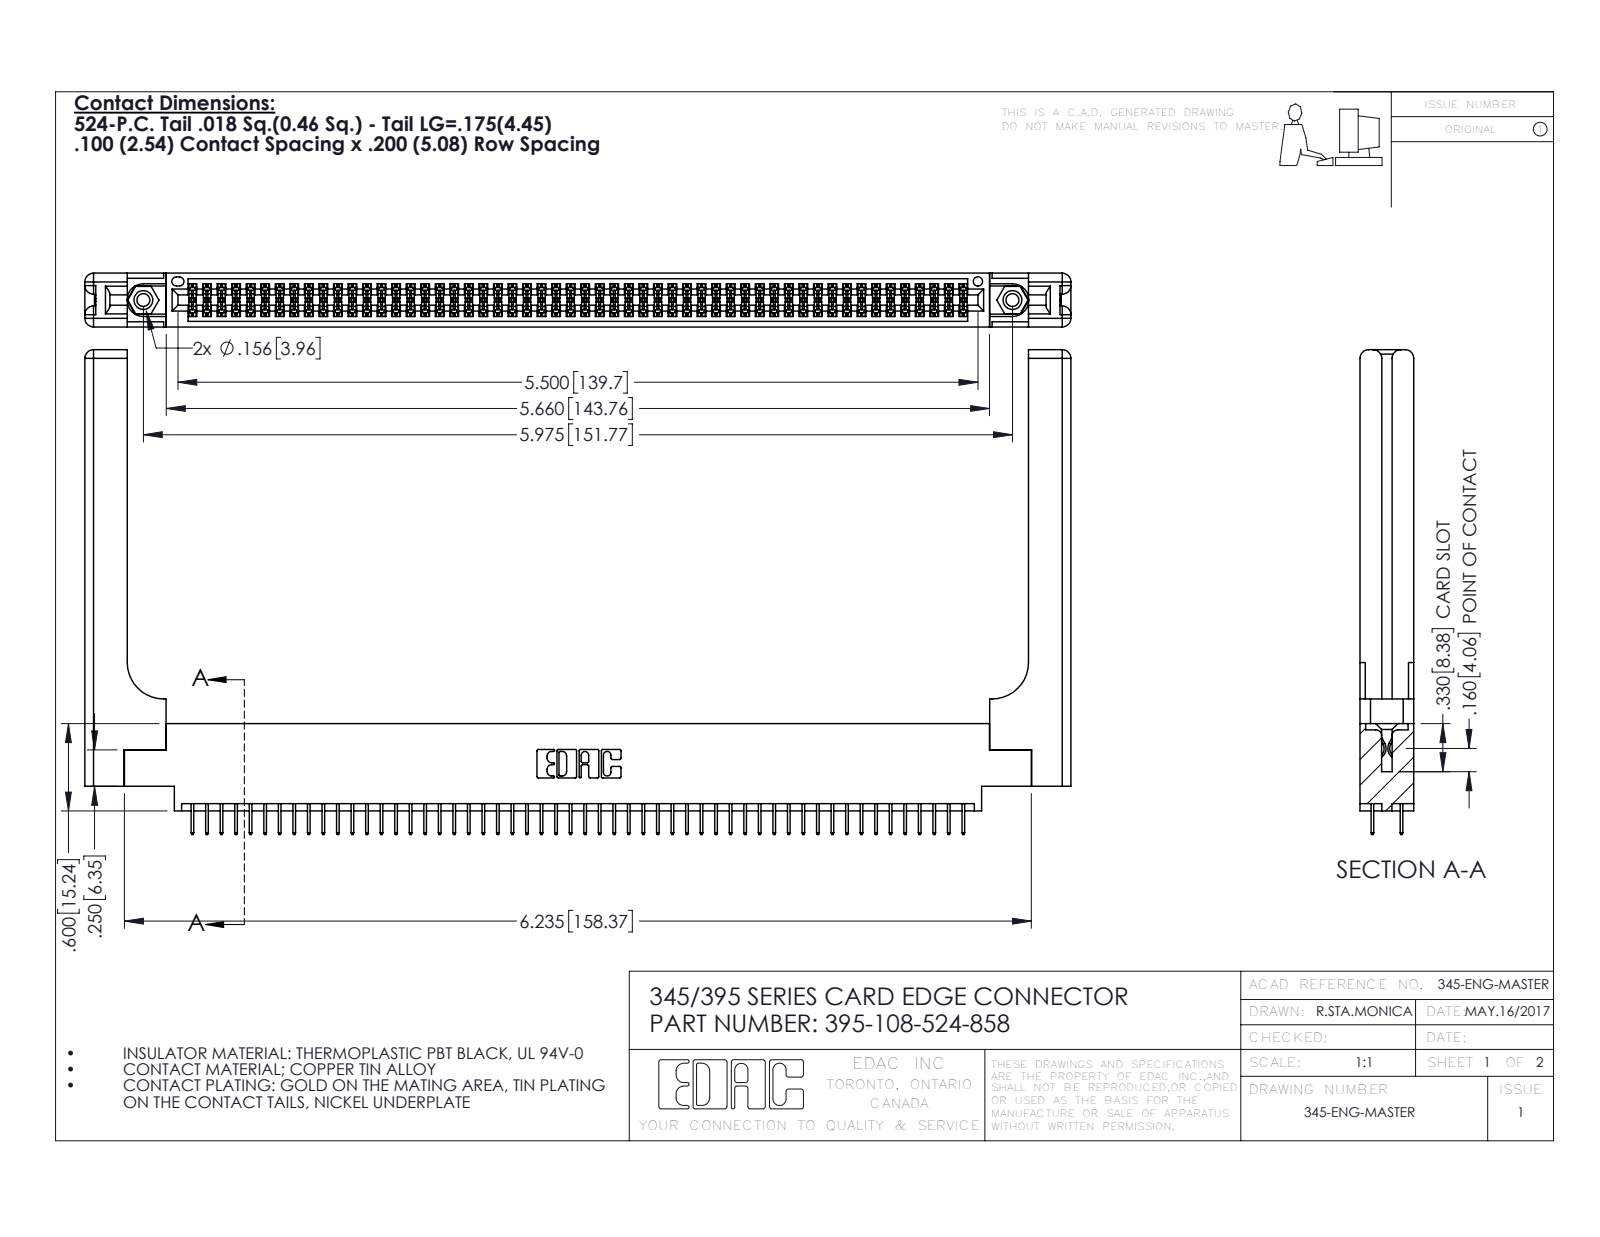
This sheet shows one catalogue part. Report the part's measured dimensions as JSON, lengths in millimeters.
{"part_name": "345 Part_0.170 Offset - 0.156 Dia-TH; 345-220-058_345-220-058; 395-108-524-858; 345-292-001_345-293-124 (+1 more)", "step_written_by": "SolidWorks 2016 (CONFIG_CONTROL_DESIGN)", "units": "millimeters", "bodies": {"solids": 113, "faces": 6218, "planar": 4444, "cylindrical": 1714, "other": 60}, "overall_size": [172.2, 84.6, 9.4], "volume_mm3": 25040, "surface_area_mm2": 29480, "round_holes": [[2.3, 2], [3.2, 2], [4, 2], [1.6, 1]], "round_bosses_or_shafts": [[3.9, 2]], "partial_cylinders_radius": [[0.2, 162], [0.3, 22], [1.5, 16], [0.2, 6], [0.8, 6], [0.7, 3], [0.4, 2], [0.5, 2]], "face_to_face_distances": [1.8, 9.4, 7.6, 5.1, 2.5, 6.9, 0.6, 5.7, 4.4, 3.8], "hole_center_spacings": [6.9, 145.8, 151.8]}
